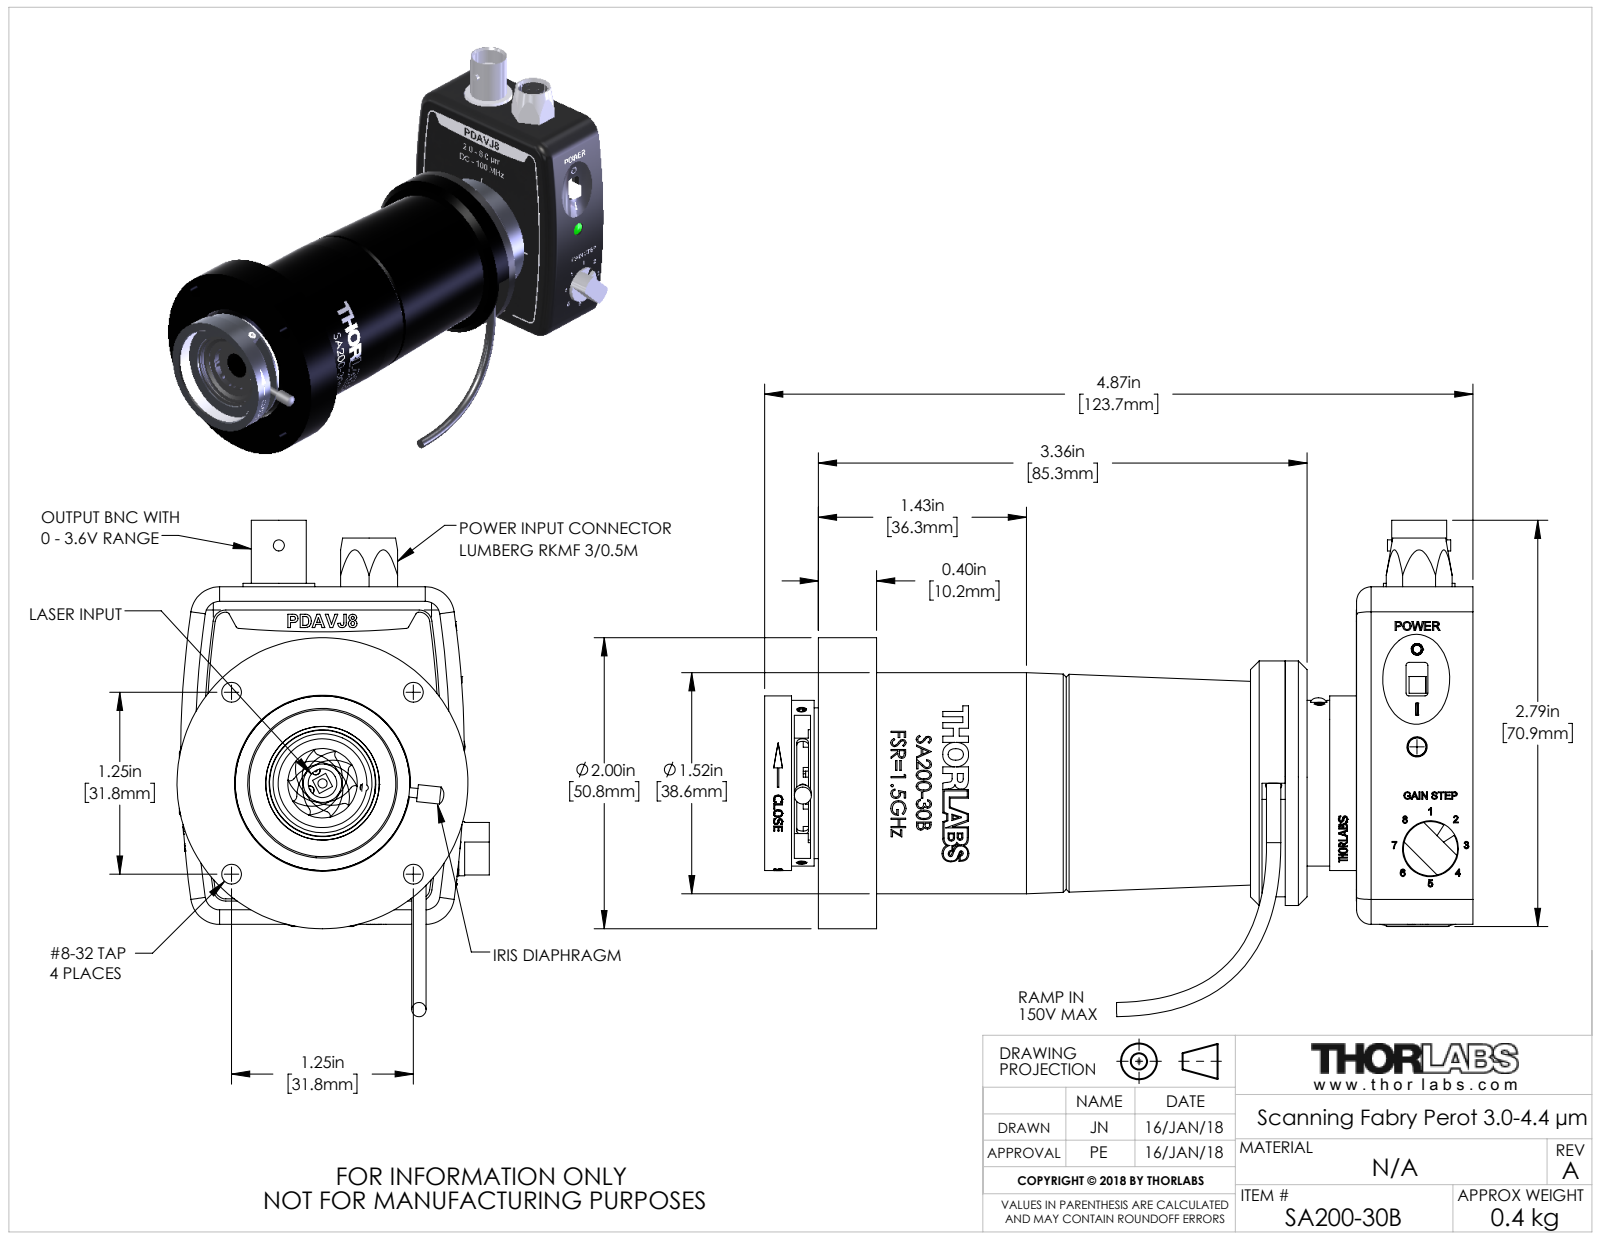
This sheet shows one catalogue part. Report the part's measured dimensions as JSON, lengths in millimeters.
{"part_name": "SM1CP2; SA200-3-CT; SA200-30B; PDAVJ8-Solidworks (+4 more)", "step_written_by": "SolidWorks 2016 (AUTOMOTIVE_DESIGN)", "units": "millimeters", "bodies": {"solids": 109, "faces": 4017, "planar": 1812, "cylindrical": 799, "other": 1406}, "overall_size": [126.46, 71.3, 66.16], "volume_mm3": 71296, "surface_area_mm2": 65742, "round_holes": [[1.68, 20], [1.78, 7], [3.45, 4], [1, 3], [0.45, 2], [1.1, 2], [1.5, 2], [1.6, 2], [3.3, 2], [0.38, 1], [0.89, 1], [1.27, 1]], "round_bosses_or_shafts": [[1.52, 20], [1.65, 12], [1.65, 10], [2.18, 8], [5, 4], [2.98, 2], [1.63, 2], [50.8, 1]], "partial_cylinders_radius": [[0.83, 20], [0.85, 20], [1.61, 20], [6.38, 20], [9.6, 20], [0.51, 18], [0.76, 8], [2.54, 8]], "face_to_face_distances": [1.5, 1.78, 12.45, 93.98, 18.72, 20.22, 16.94, 18.44, 95.76, 112.7], "hole_center_spacings": [14.11, 12, 7.42, 14.83, 4.58, 4.64, 8.67, 8.72]}
